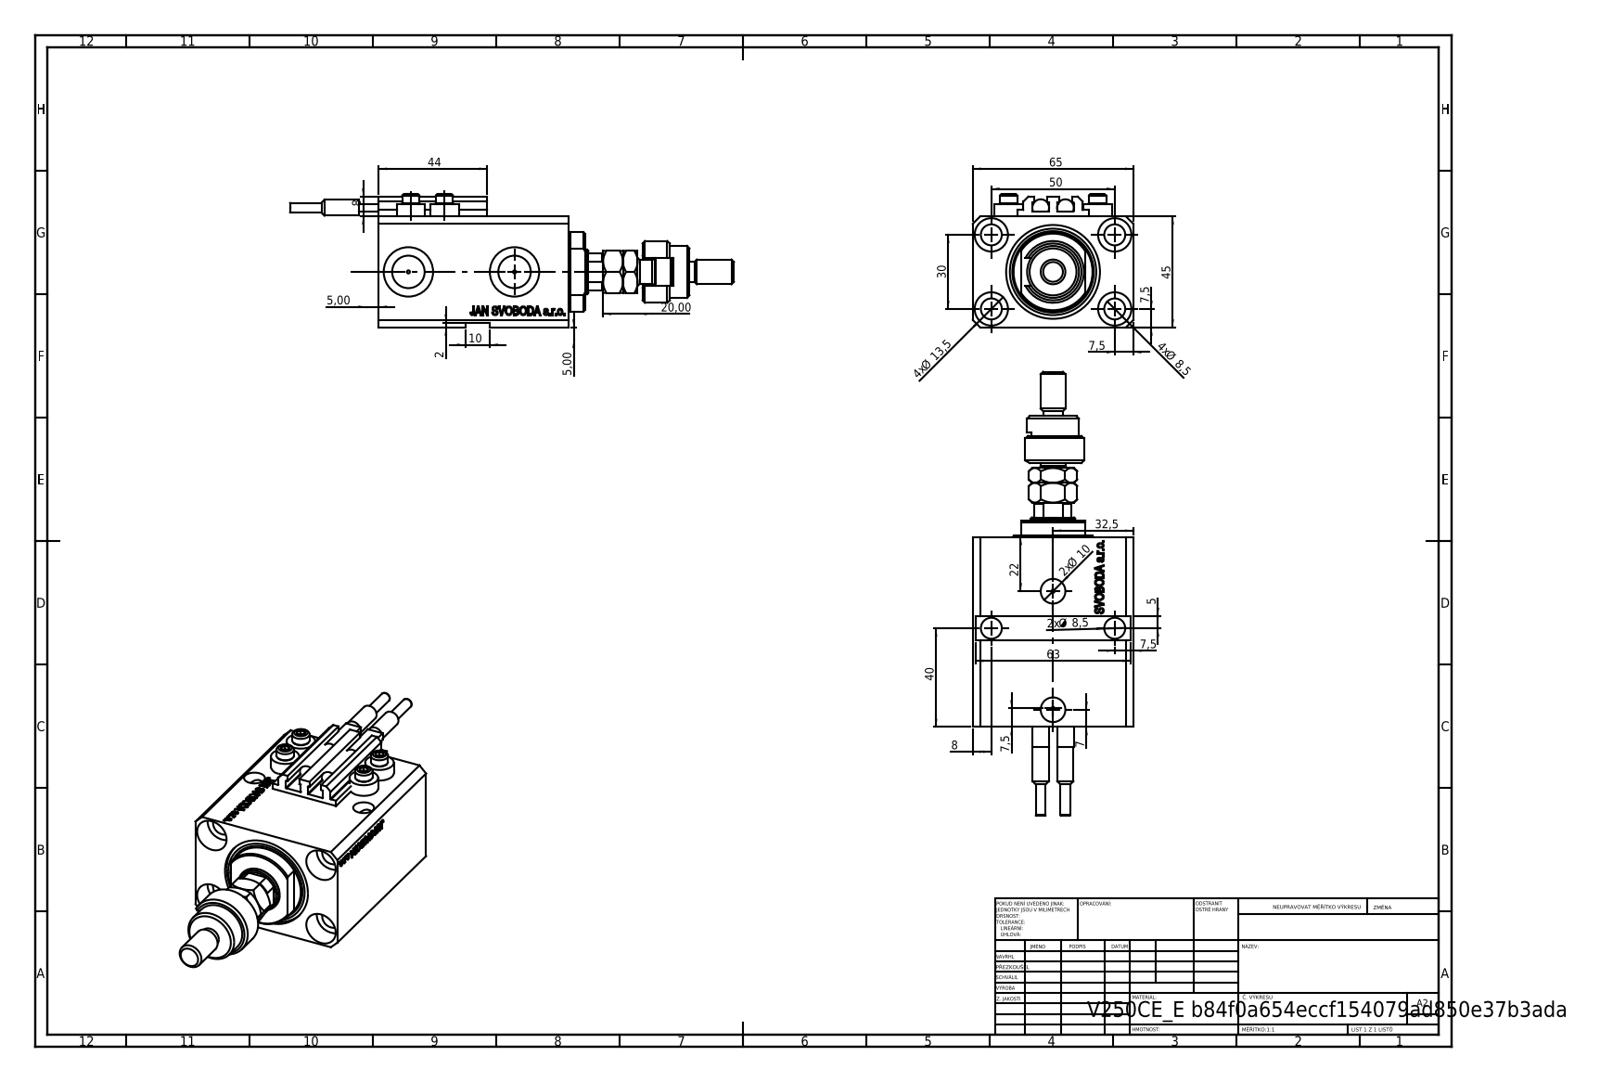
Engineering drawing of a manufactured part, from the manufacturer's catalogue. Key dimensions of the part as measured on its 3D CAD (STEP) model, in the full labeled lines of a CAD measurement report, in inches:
Part name (STEP PRODUCT): V250CE_VC_E; ALLEN BOLT V250CE; MFA; SWITCH_V250CE (+3 more)
STEP written by: SolidWorks 2019 (CONFIG_CONTROL_DESIGN)
Units: inches
Bodies: 12 solids, 1204 faces (571 planar, 151 cylindrical, 482 other)
Overall size (bounding box): 7.083 × 2.559 × 2.126
Volume: 13.13 in³ · Surface area: 107.7 in²
Round holes (diameter × count): ⌀0.335 ×7, ⌀0.049 ×4, ⌀0.157 ×4, ⌀0.531 ×4, ⌀0.394 ×2, ⌀0.518 ×2, ⌀0.787 ×2, ⌀0.709 ×1, ⌀1.496 ×1
Round bosses / shafts (diameter × count): ⌀0.457 ×4, ⌀0.276 ×4, ⌀0.268 ×2, ⌀0.256 ×2, ⌀0.157 ×2, ⌀0.984 ×1, ⌀0.827 ×1, ⌀0.63 ×1
Partial cylindrical surfaces — rounded edges, fillets, slot ends (radius × count): R0.008 ×10, R0.217 ×1, R0.335 ×1, R0.344 ×1, R0.63 ×1
Main face-to-face distances: 1.772, 2.559, 2.043, 0.079, 0.988, 0.118, 3.031, 0.272, 1.85, 2.76
Hole centre spacings: 1.148, 1.969, 0.535, 0.595, 0.741, 0.747, 1.032, 1.048
